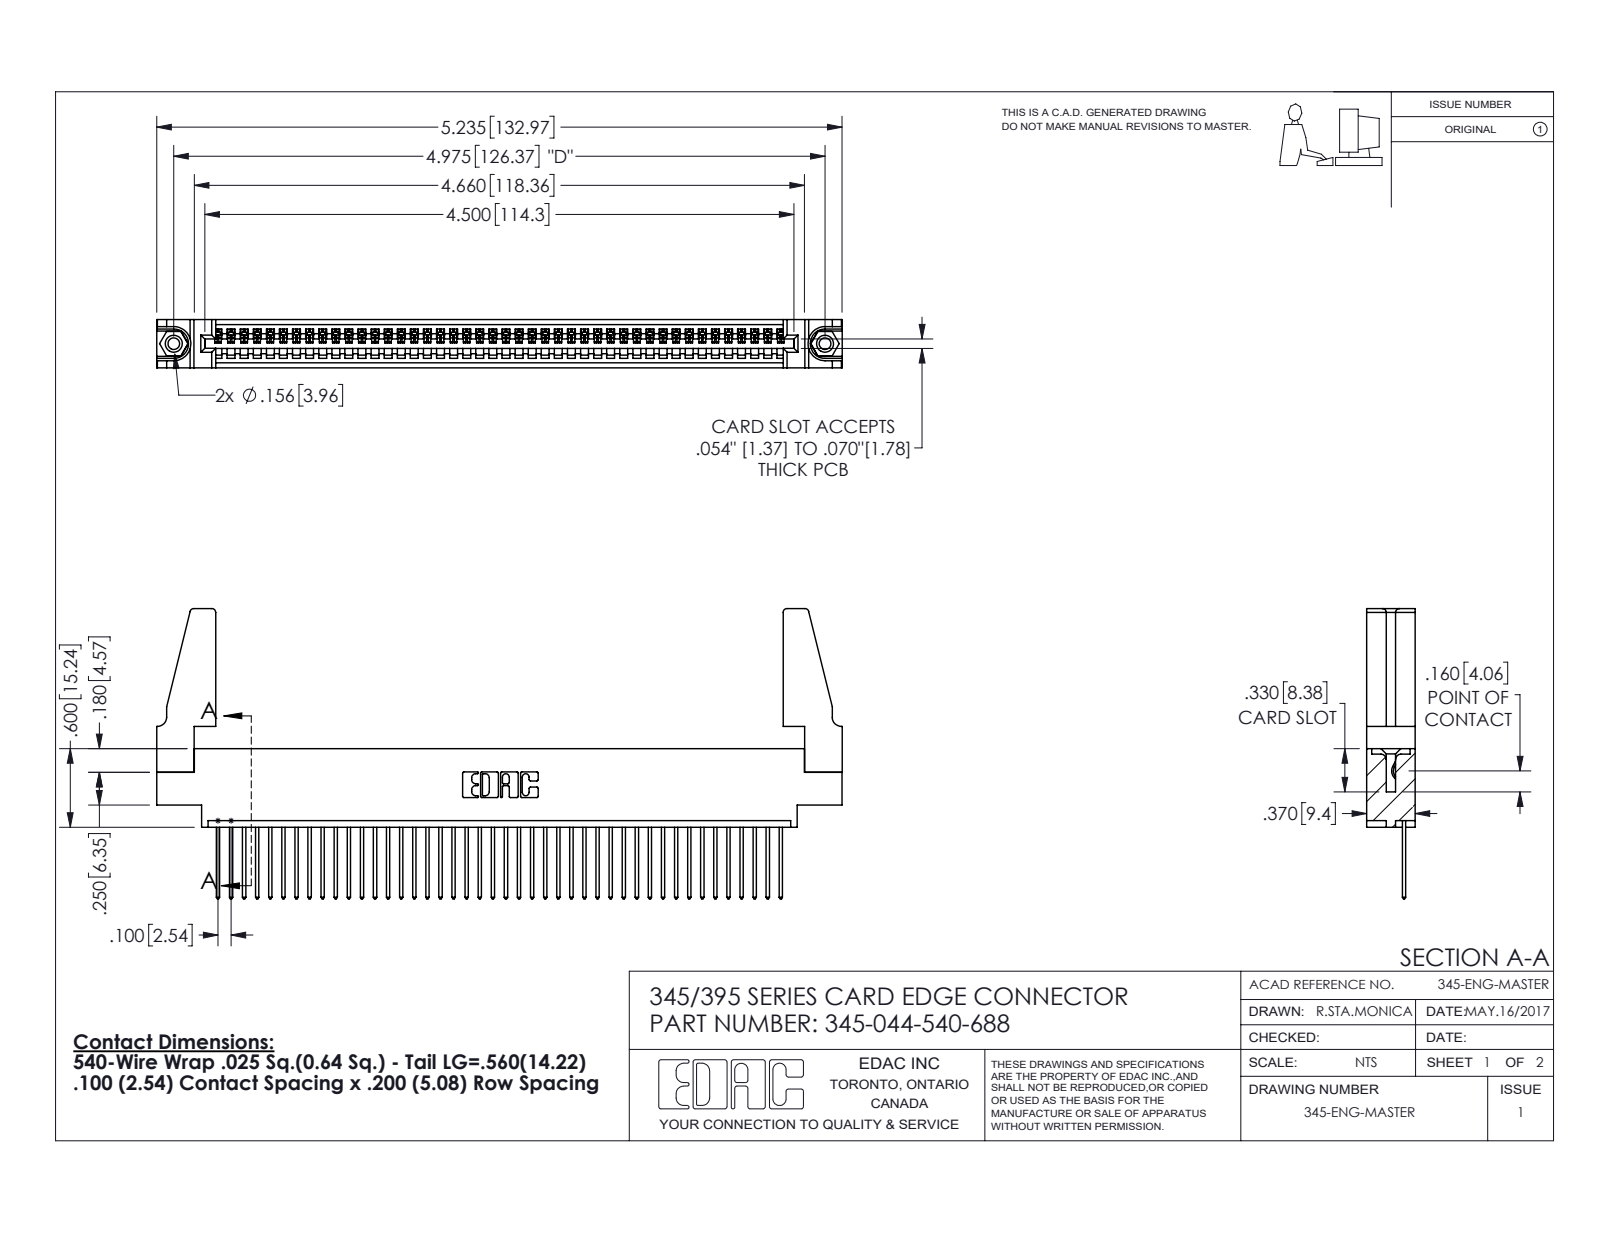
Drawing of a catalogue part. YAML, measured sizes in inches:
part_name: "345-220-078_345-220-088; 345-044-540-688; 345-292-001_345-293-140; 345-250-001_345-250-001-102 (+1 more)"
step_written_by: "SolidWorks 2016 (CONFIG_CONTROL_DESIGN)"
units: inches
bodies: {solids: 49, faces: 2806, planar: 1916, cylindrical: 874, other: 16}
overall_size: [5.236, 2.217, 0.37]
volume: 0.967
surface_area: 31.7
round_holes:
  - {diameter: 0.089, count: 2}
  - {diameter: 0.125, count: 2}
  - {diameter: 0.156, count: 2}
  - {diameter: 0.064, count: 1}
round_bosses_or_shafts:
  - {diameter: 0.155, count: 2}
partial_cylinders:
  - {radius: 0.006, count: 88}
  - {radius: 0.01, count: 88}
  - {radius: 0.01, count: 22}
  - {radius: 0.03, count: 8}
  - {radius: 0.007, count: 6}
  - {radius: 0.031, count: 6}
  - {radius: 0.026, count: 3}
  - {radius: 0.031, count: 2}
face_to_face_distances: [0.072, 0.298, 0.37, 0.098, 0.272, 0.025, 0.2, 0.225, 0.175, 0.149]
hole_center_spacings: [0.27, 4.739, 4.975]
